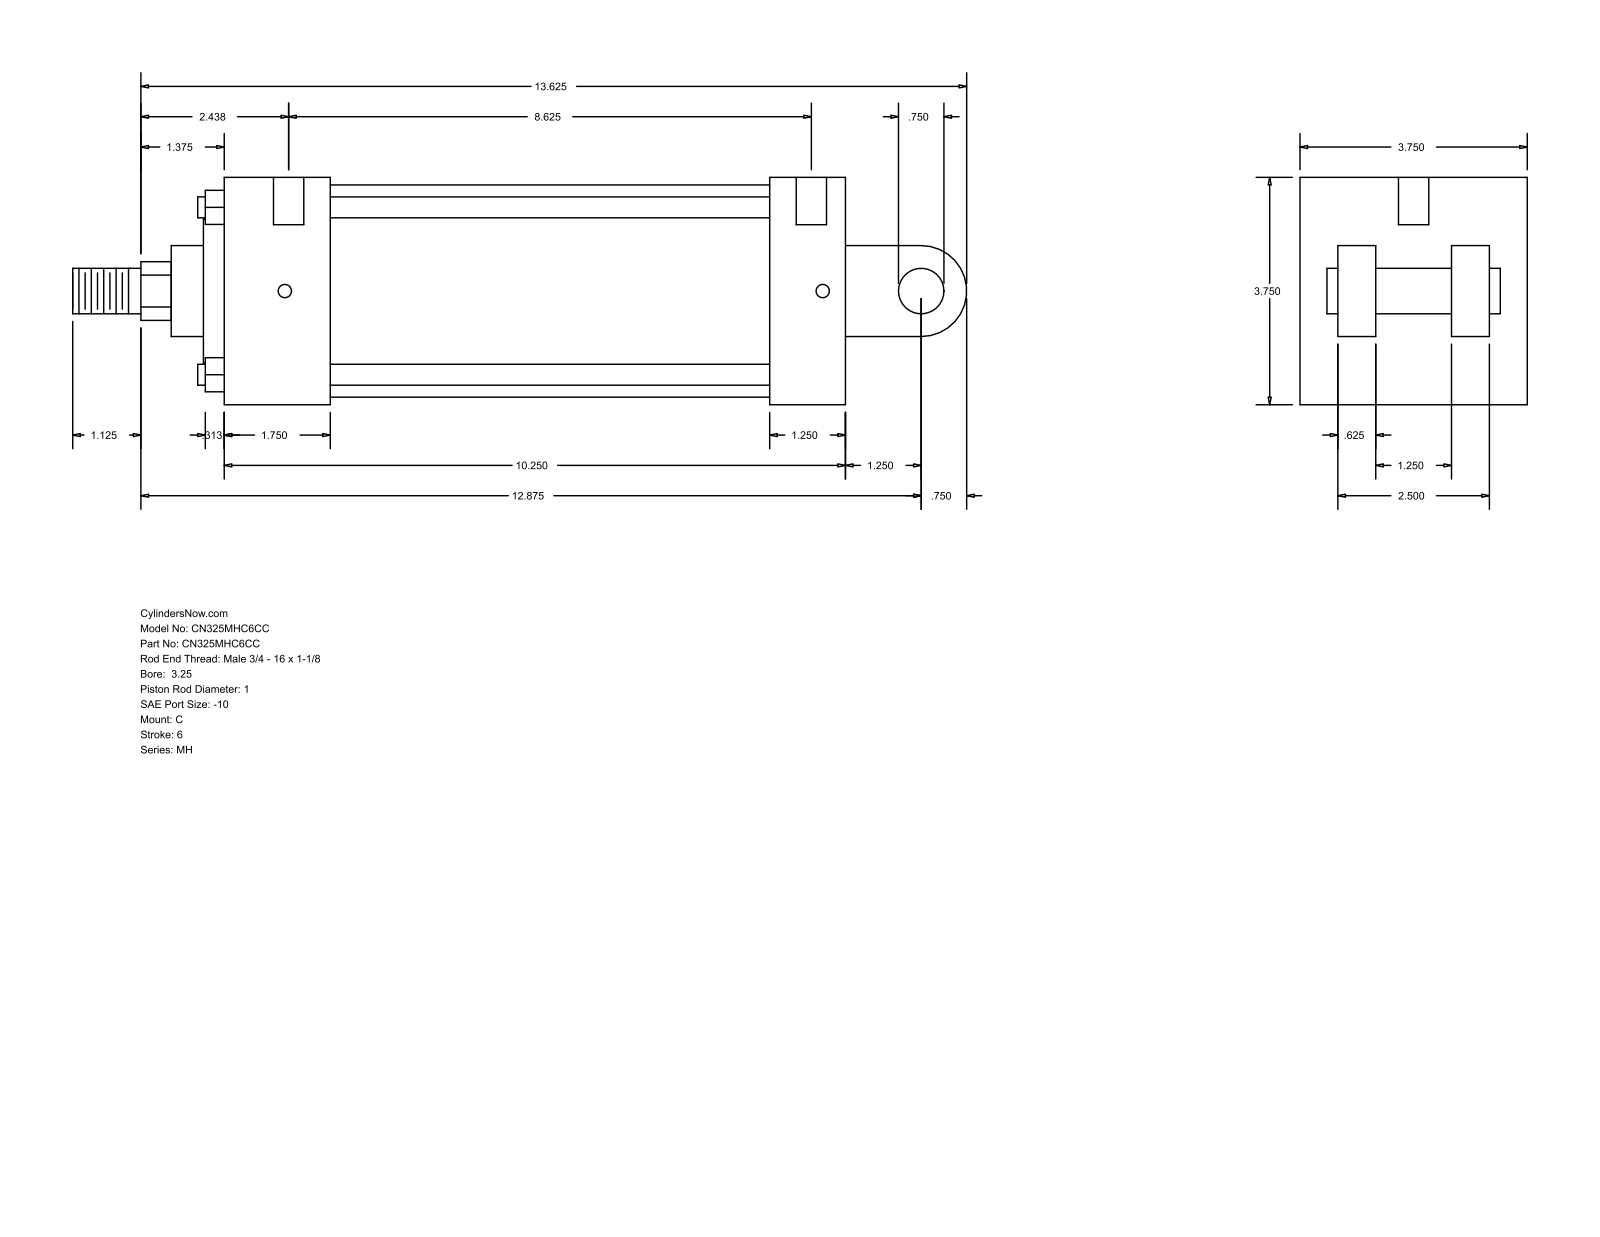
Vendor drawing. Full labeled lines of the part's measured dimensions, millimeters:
Part name (STEP PRODUCT): MH_C__0325_1
STEP written by: GSSL Pune (CONFIG_CONTROL_DESIGN)
Units: millimetres
Bodies: 0 solids, 101 faces (71 planar, 30 cylindrical, 0 other)
Overall size (bounding box): 374.65 × 95.25 × 95.25
Round holes (diameter × count): ⌀5.56 ×4, ⌀12.7 ×2
Round bosses / shafts (diameter × count): ⌀8.76 ×4, ⌀19.05 ×2, ⌀88.9 ×1, ⌀60.33 ×1, ⌀38.1 ×1, ⌀25.4 ×1
Partial cylindrical surfaces — rounded edges, fillets, slot ends (radius × count): R12.29 ×1, R19.05 ×1
Main face-to-face distances: 95.24, 15.87, 260.35, 63.5, 79.37, 31.74, 47.63, 44.46, 228.6, 184.14
Hole centre spacings: 225.42, 1.58, 4.76, 219.08, 220.66, 223.84
